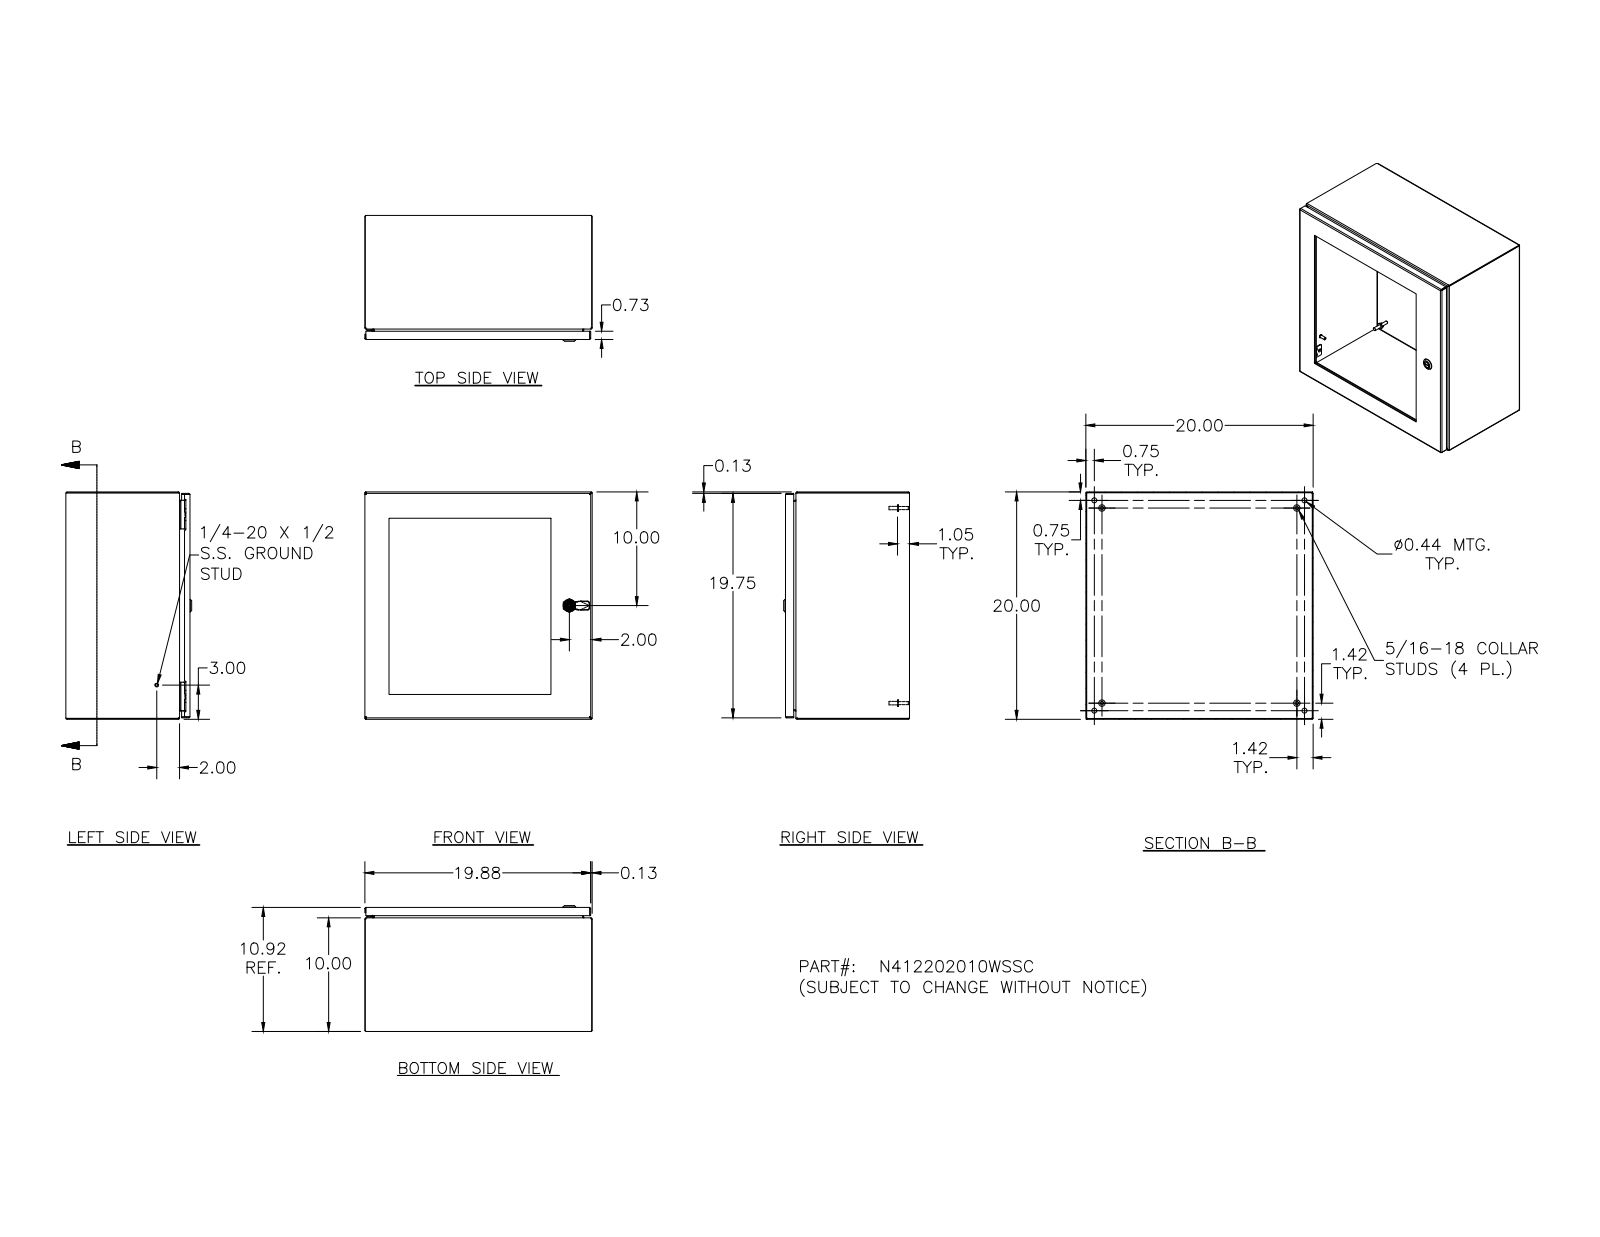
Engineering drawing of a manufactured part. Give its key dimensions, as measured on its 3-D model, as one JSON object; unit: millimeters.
{"part_name": "N412202010WSSC; N412202010WSSCBKP; N4122020WSSCLID; HFW328176 (+8 more)", "step_written_by": "Autodesk Inventor 2011 (AUTOMOTIVE_DESIGN)", "units": "millimeters", "bodies": {"solids": 70, "faces": 1940, "planar": 754, "cylindrical": 565, "other": 621}, "overall_size": [508, 508, 281.3], "volume_mm3": 2987000, "surface_area_mm2": 2441000, "round_holes": [[4, 18], [7.1, 16], [2.4, 4], [3.9, 4], [4.2, 4], [4.4, 4], [4.8, 4], [11.1, 4], [4.7, 1], [5, 1], [8, 1], [10, 1]], "round_bosses_or_shafts": [[4.8, 16], [6.4, 15], [6.4, 10], [14.3, 4], [9.1, 4], [8.1, 4], [7.6, 4], [7, 4]], "partial_cylinders_radius": [[0.8, 34], [1.3, 26], [2.7, 24], [0.4, 18], [3.2, 16], [0.5, 9], [0.8, 8], [4, 4]], "face_to_face_distances": [1.9, 506.1, 275.4, 273.5, 508, 504.2, 6.4, 269.1, 267.2, 277.3], "hole_center_spacings": [101.6, 203.2, 406.6, 406.4, 437.4, 158, 218.1, 254.9]}
